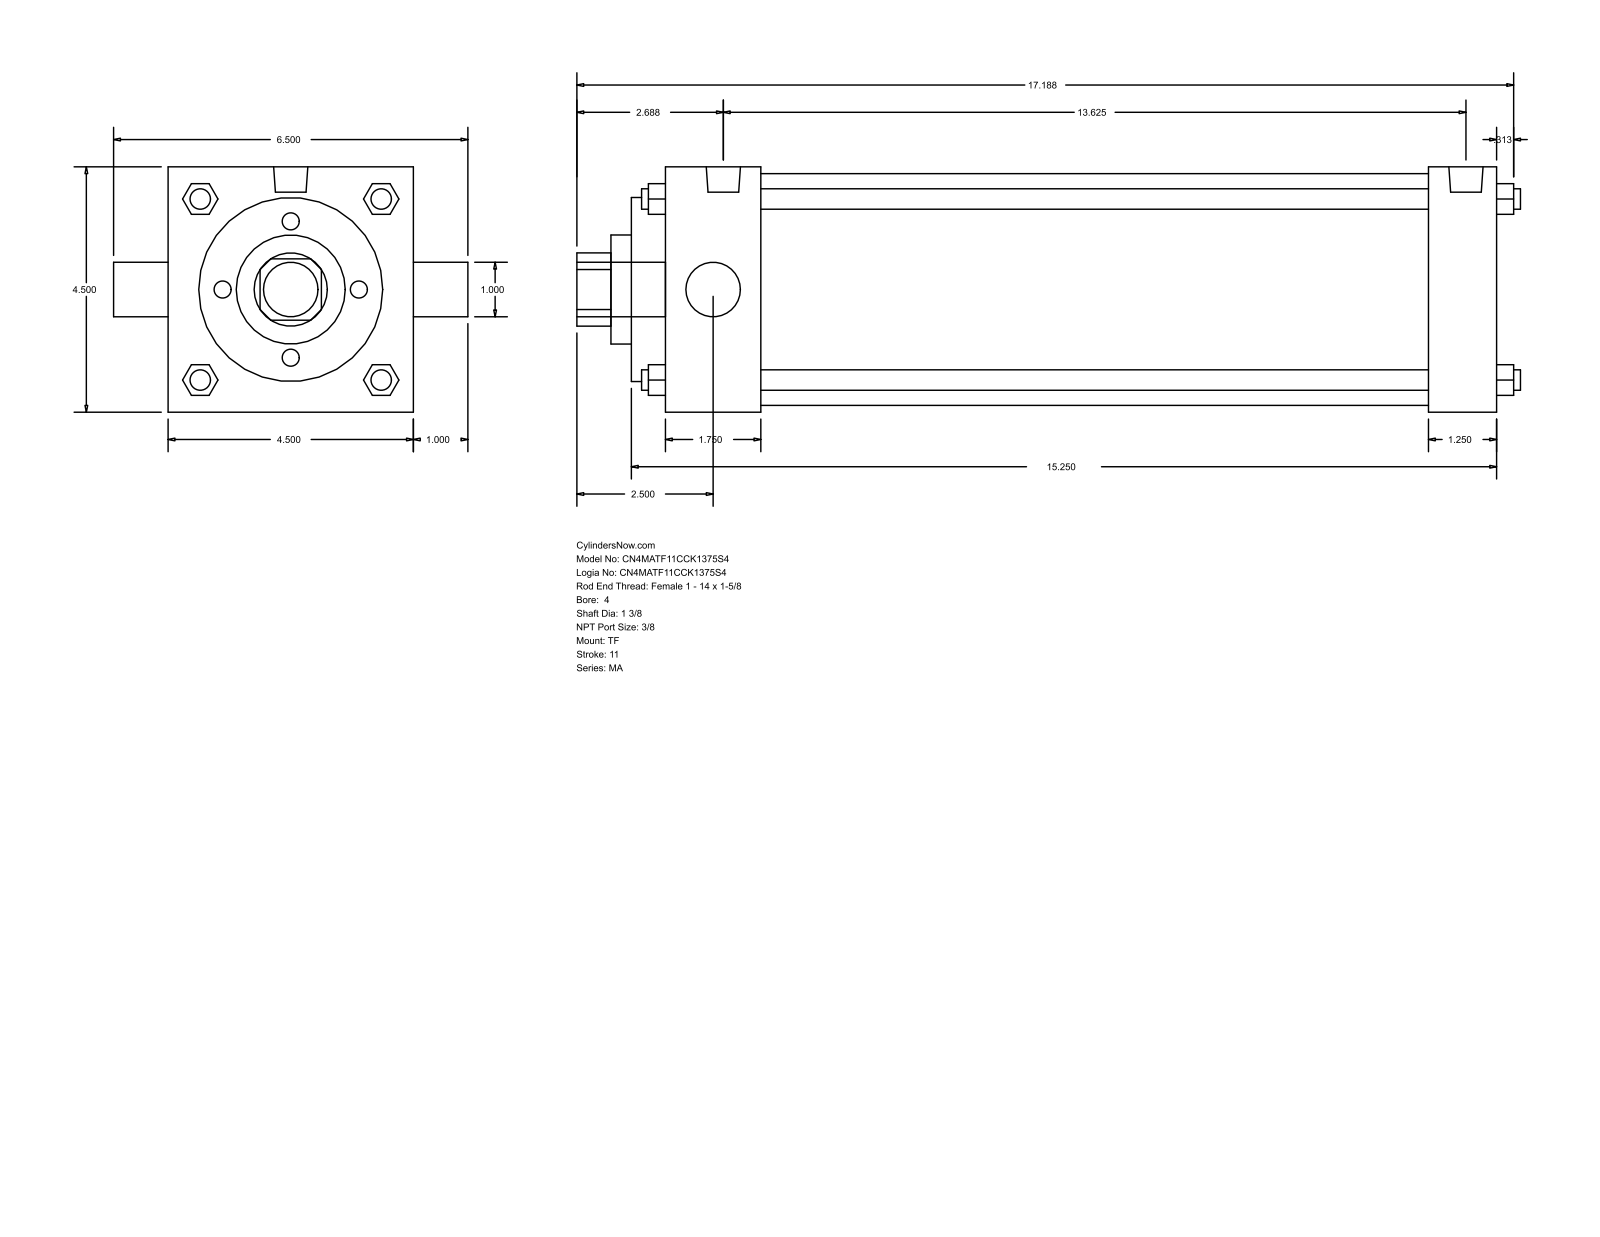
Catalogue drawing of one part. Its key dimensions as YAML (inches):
part_name: "MA_TF__0400_1.375"
step_written_by: "GSSL Pune (CONFIG_CONTROL_DESIGN)"
units: inches
bodies: {solids: 0, faces: 122, planar: 93, cylindrical: 29, other: 0}
overall_size: [17.313, 6.5, 4.5]
round_holes:
  - {diameter: 1, count: 1}
  - {diameter: 1.375, count: 1}
  - {diameter: 2, count: 1}
  - {diameter: 3.375, count: 1}
  - {diameter: 4.25, count: 1}
round_bosses_or_shafts:
  - {diameter: 0.375, count: 4}
  - {diameter: 0.437, count: 3}
  - {diameter: 0.627, count: 2}
  - {diameter: 1, count: 1}
partial_cylinders:
  - {radius: 0.672, count: 1}
face_to_face_distances: [4.5, 15.25, 15.875, 0.625, 14.625, 14, 1.25, 2.375, 1.75, 12.25]
